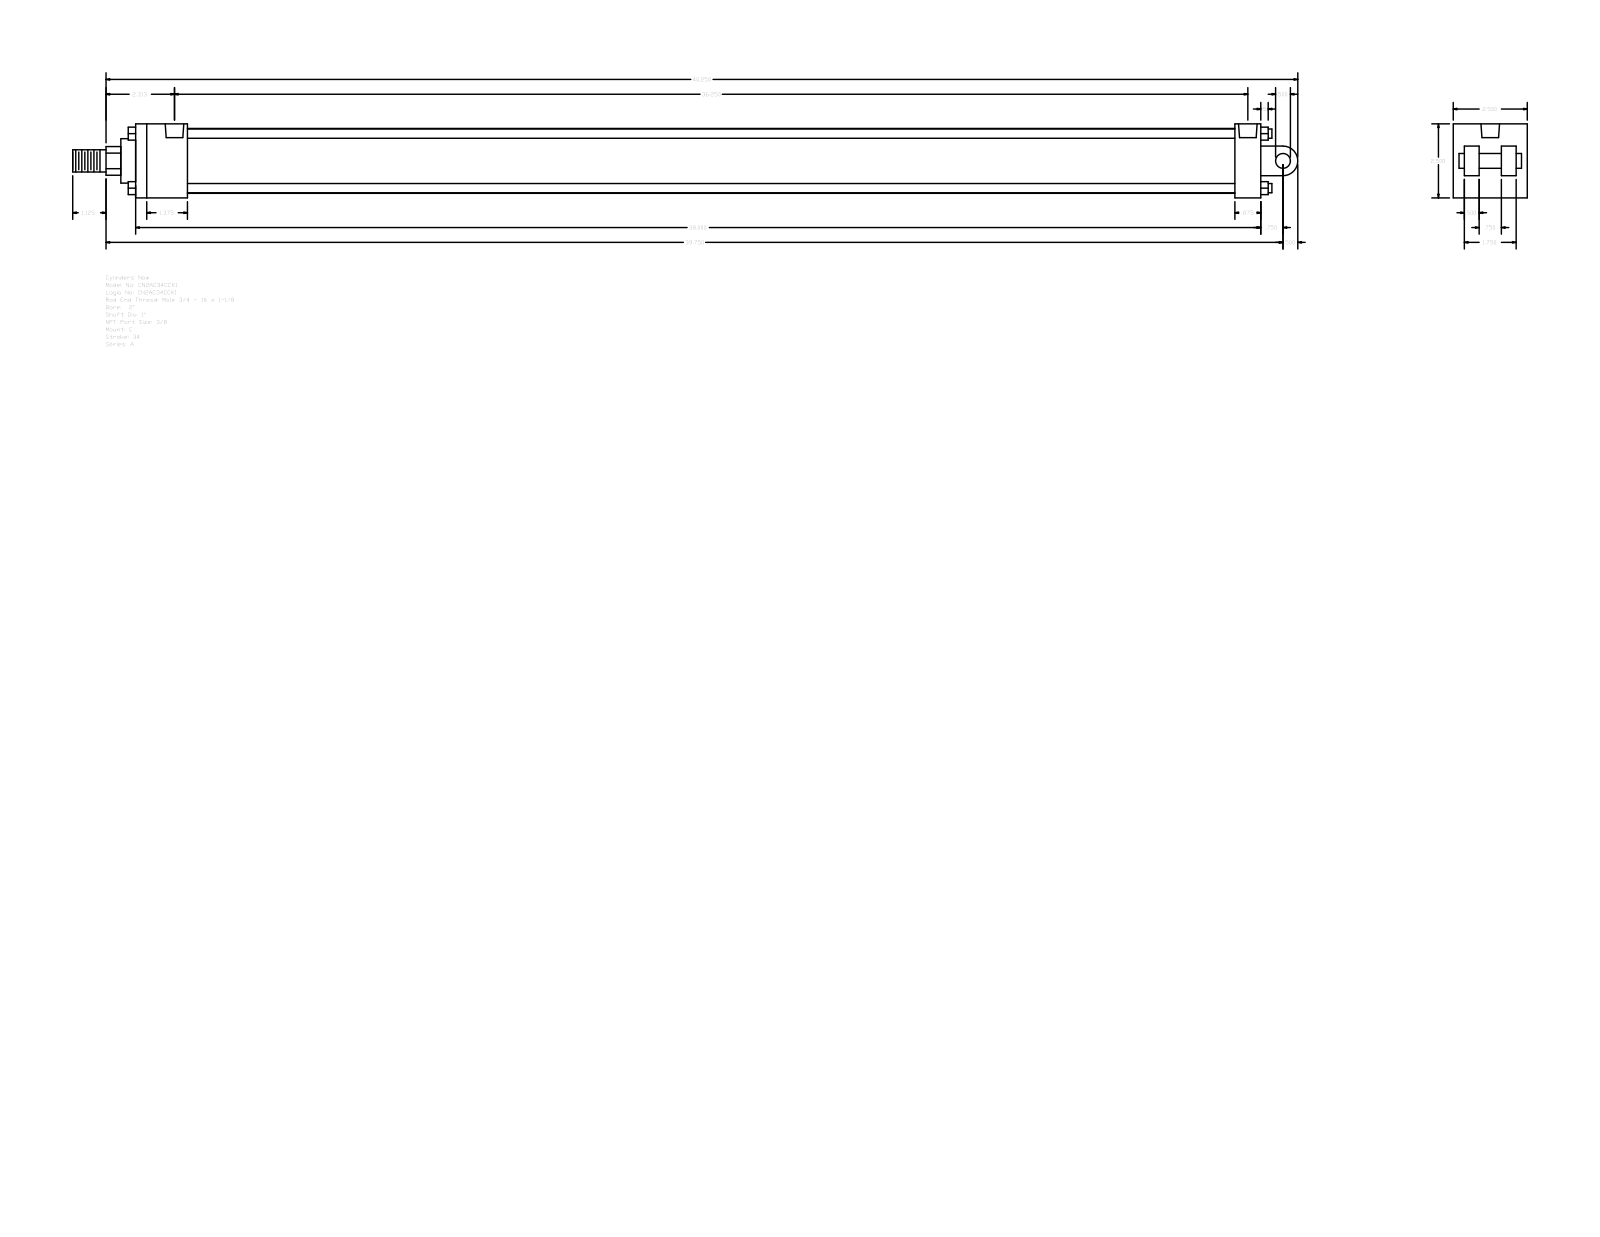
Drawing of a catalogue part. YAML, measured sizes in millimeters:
part_name: "A_C__0200_1"
step_written_by: "GSSL Pune (CONFIG_CONTROL_DESIGN)"
units: millimeters
bodies: {solids: 0, faces: 135, planar: 102, cylindrical: 33, other: 0}
overall_size: [1050.92, 63.5, 63.5]
round_holes:
  - {diameter: 5.56, count: 4}
  - {diameter: 15.93, count: 2}
round_bosses_or_shafts:
  - {diameter: 7.94, count: 4}
  - {diameter: 55.63, count: 1}
  - {diameter: 38.1, count: 1}
  - {diameter: 25.4, count: 1}
  - {diameter: 19.05, count: 1}
  - {diameter: 12.7, count: 1}
partial_cylinders:
  - {radius: 12.29, count: 1}
  - {radius: 12.7, count: 1}
face_to_face_distances: [63.5, 22.22, 965.2, 44.45, 12.7, 9.52, 920.75, 942.98, 898.53, 53.98]
hole_center_spacings: [915.18, 1.59, 3.98, 916.77, 919.16, 920.75]
